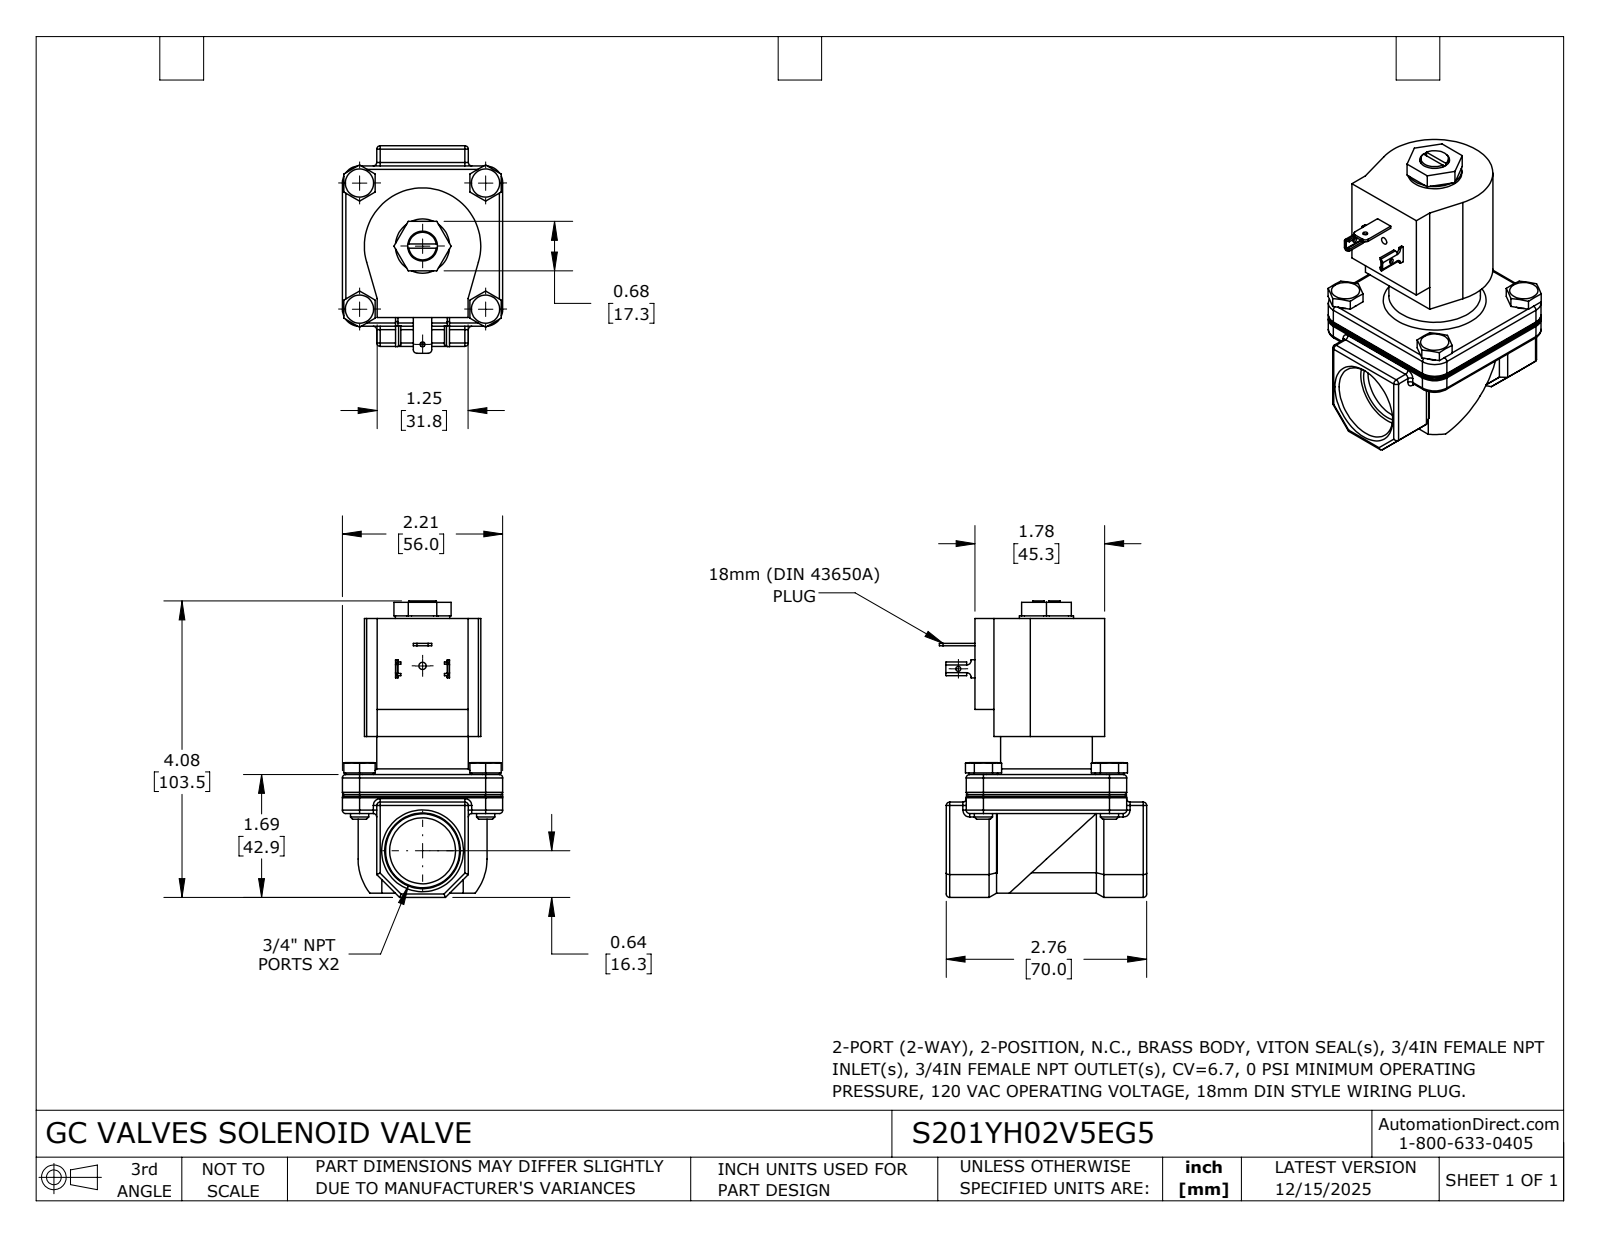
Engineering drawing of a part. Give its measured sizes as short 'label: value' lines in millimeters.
name: S201YH02V5EG5
written by: SolidWorks 2024 (CONFIG_CONTROL_DESIGN)
unit: mm
bodies: 1 solid, 338 faces (166 planar, 112 cylindrical, 60 other)
size: 103.5 × 72.4 × 56
volume: 166 500 mm³; area: 28 280 mm²
holes: 1× ⌀1.7, 1× ⌀1.7, 1× ⌀2.5, 1× ⌀10.4, 1× ⌀23
bosses: 4× ⌀9.9, 4× ⌀6.4, 1× ⌀32, 1× ⌀18.9, 1× ⌀9.7
rounds: 34× R1.2, 4× R0.2, 4× R0.8, 4× R1, 4× R5.9, 4× R6, 2× R1.3, 2× R1.5
face distances: 1.5, 54.4, 12, 44, 13.6, 68.1, 56, 27.8, 41.4, 95.9
hole spacings: 34.3, 64.5
